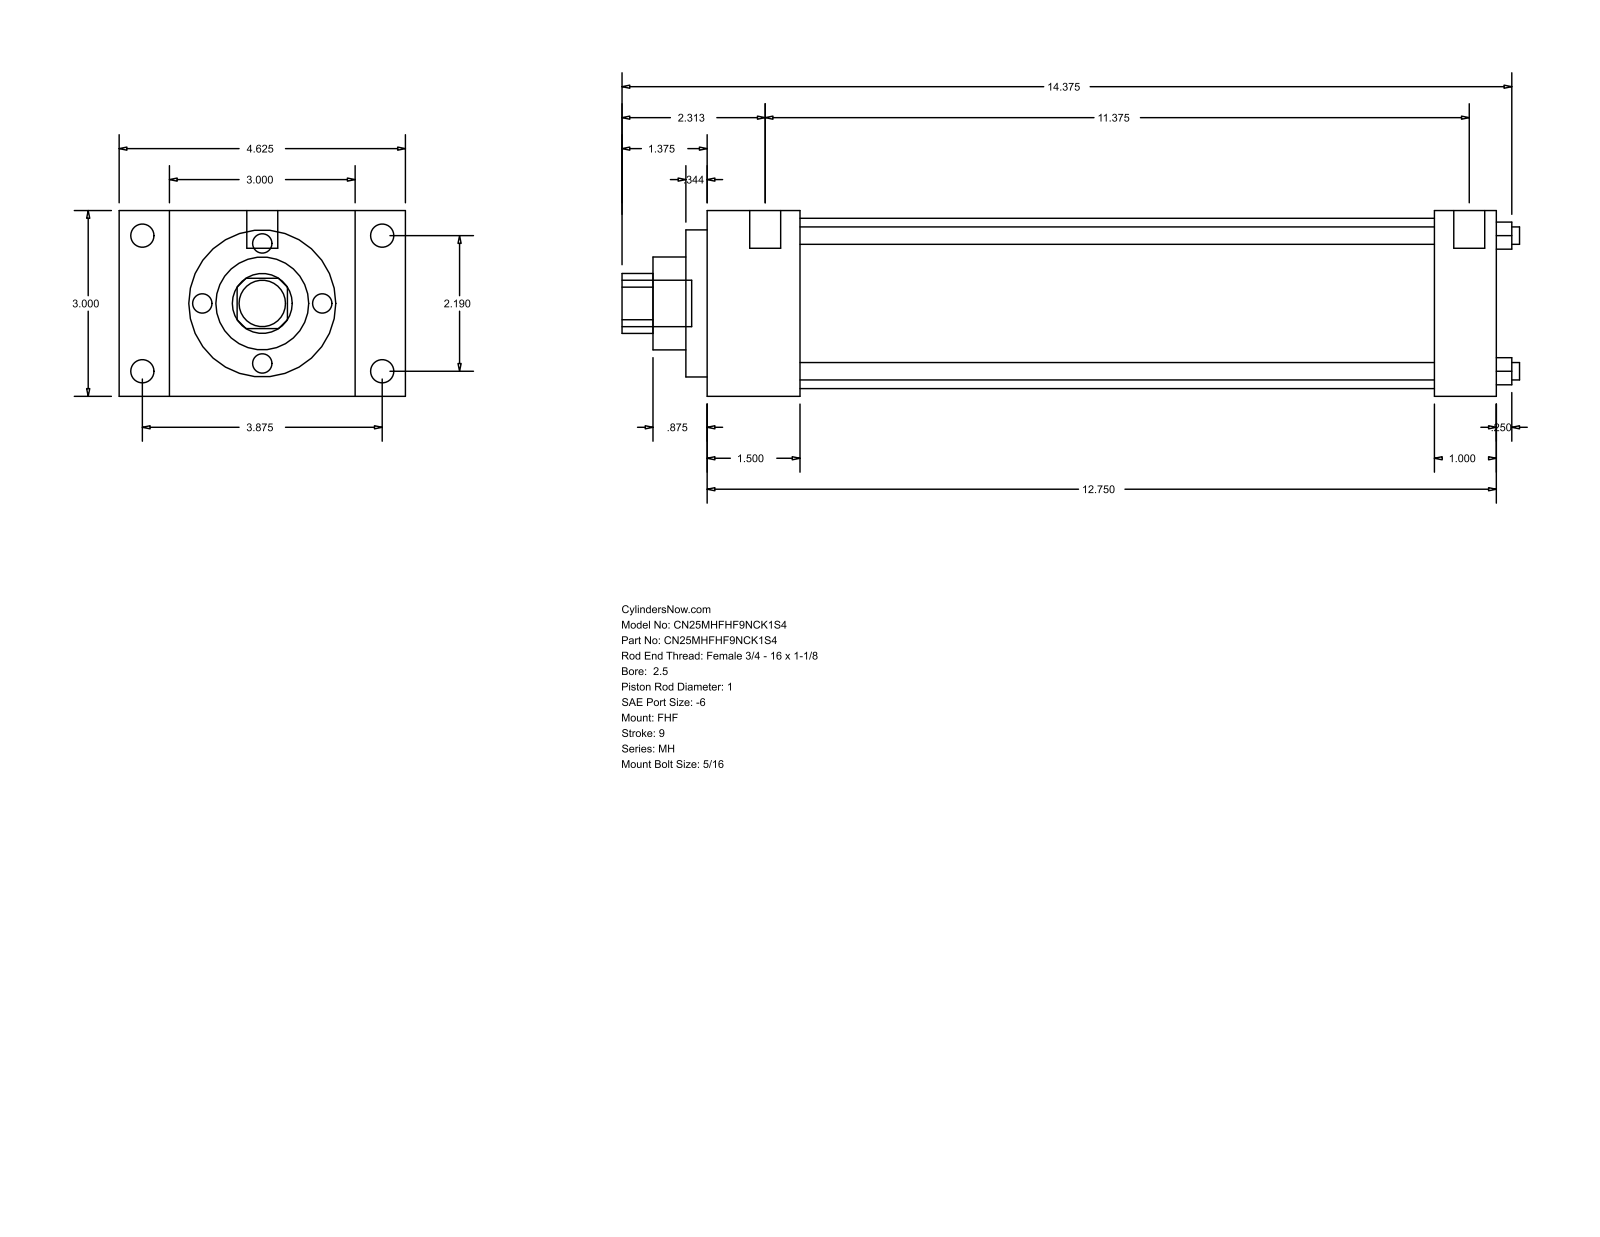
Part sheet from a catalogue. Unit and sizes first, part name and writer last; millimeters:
Units: millimetres
Overall size (bounding box): 368.3 × 117.47 × 76.2
Round holes (diameter × count): ⌀7.14 ×4, ⌀25.4 ×1, ⌀38.1 ×1, ⌀60.33 ×1, ⌀69.85 ×1
Round bosses / shafts (diameter × count): ⌀9.53 ×4, ⌀5.56 ×4, ⌀12.7 ×2, ⌀19.05 ×1
Partial cylindrical surfaces — rounded edges, fillets, slot ends (radius × count): R12.29 ×1
Main face-to-face distances: 76.2, 323.85, 38.11, 285.74, 20.64, 96.84, 117.48, 25.39, 298.46, 260.35
Hole centre spacings: 39.33, 55.62, 78.66
Bodies: 0 solids, 90 faces (61 planar, 29 cylindrical, 0 other)
Part name (STEP PRODUCT): MH_FHF__0250_1
STEP written by: GSSL Pune (CONFIG_CONTROL_DESIGN)
